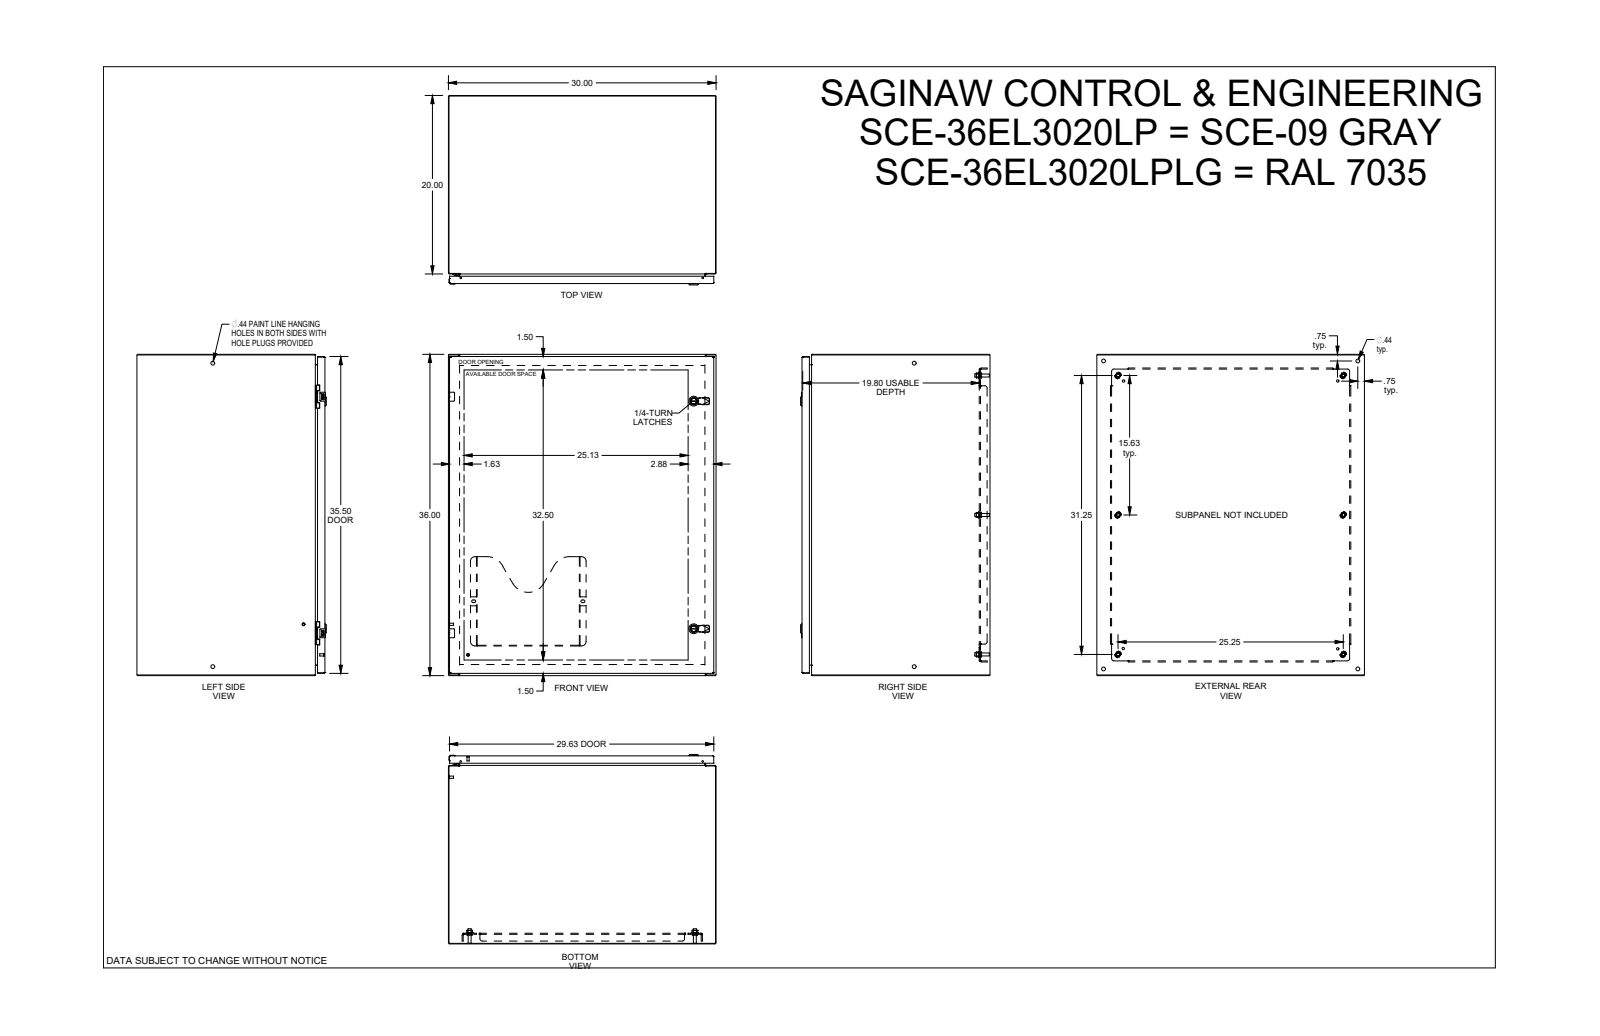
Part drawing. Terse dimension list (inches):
name: SCE-36EL3020LP
written by: SolidWorks 2021 (AUTOMOTIVE_DESIGN)
unit: in
bodies: 51 solids, 2997 faces (1139 planar, 896 cylindrical, 962 other)
size: 36 × 30 × 21.23
volume: 525.8 in³; area: 12 755 in²
holes: 6× ⌀0.367, 6× ⌀0.437, 6× ⌀0.5, 4× ⌀0.172, 4× ⌀0.205, 4× ⌀0.244, 4× ⌀0.266, 4× ⌀0.281, 4× ⌀0.375, 2× ⌀0.04, 2× ⌀0.188, 2× ⌀0.197
bosses: 6× ⌀0.366, 6× ⌀0.332, 6× ⌀0.17, 4× ⌀0.25, 4× ⌀0.248, 4× ⌀0.24, 3× ⌀0.196, 2× ⌀1.102
rounds: 56× R0.012, 40× R0.01, 20× R0.015, 20× R0.02, 17× R0.04, 13× R0.06, 12× R0.029, 12× R0.1
face distances: 0.075, 29.925, 0.075, 35.925, 0.06, 21.073, 20.998, 21.013, 20.938, 1.2
hole spacings: 0.985, 26.5, 0.02, 0.493, 0.494, 2.298, 4.493, 15.625
